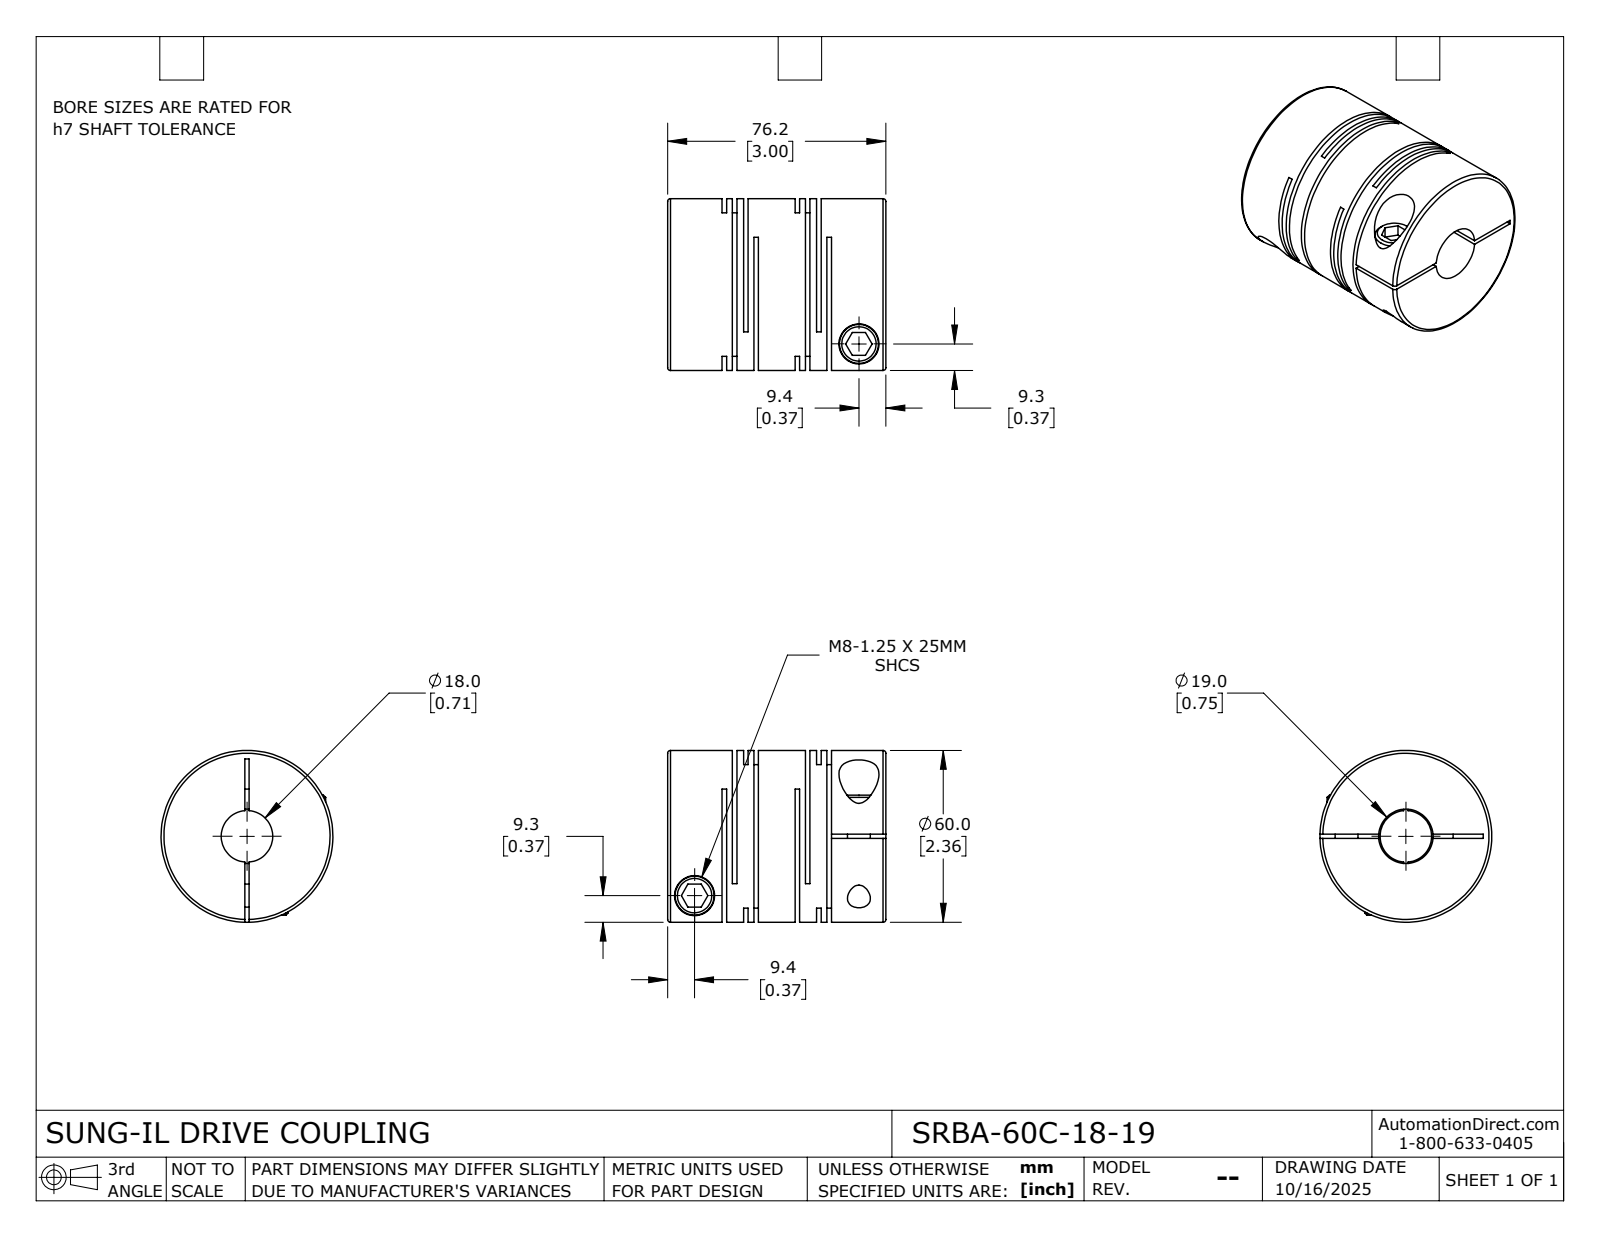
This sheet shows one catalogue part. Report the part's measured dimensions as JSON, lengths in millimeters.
{"part_name": "SRBA-60C-18-19", "step_written_by": "SolidWorks 2024 (CONFIG_CONTROL_DESIGN)", "units": "millimeters", "bodies": {"solids": 1, "faces": 115, "planar": 60, "cylindrical": 42, "other": 13}, "overall_size": [76.2, 60, 60], "volume_mm3": 162686, "surface_area_mm2": 59577, "round_holes": [[8, 2], [14, 2], [18, 1], [19, 1]], "round_bosses_or_shafts": [[13.6, 2], [60, 1]], "face_to_face_distances": [1.6, 3.6, 7.5, 25.5, 33, 2, 5.9, 3.9, 23.9, 21.9]}
